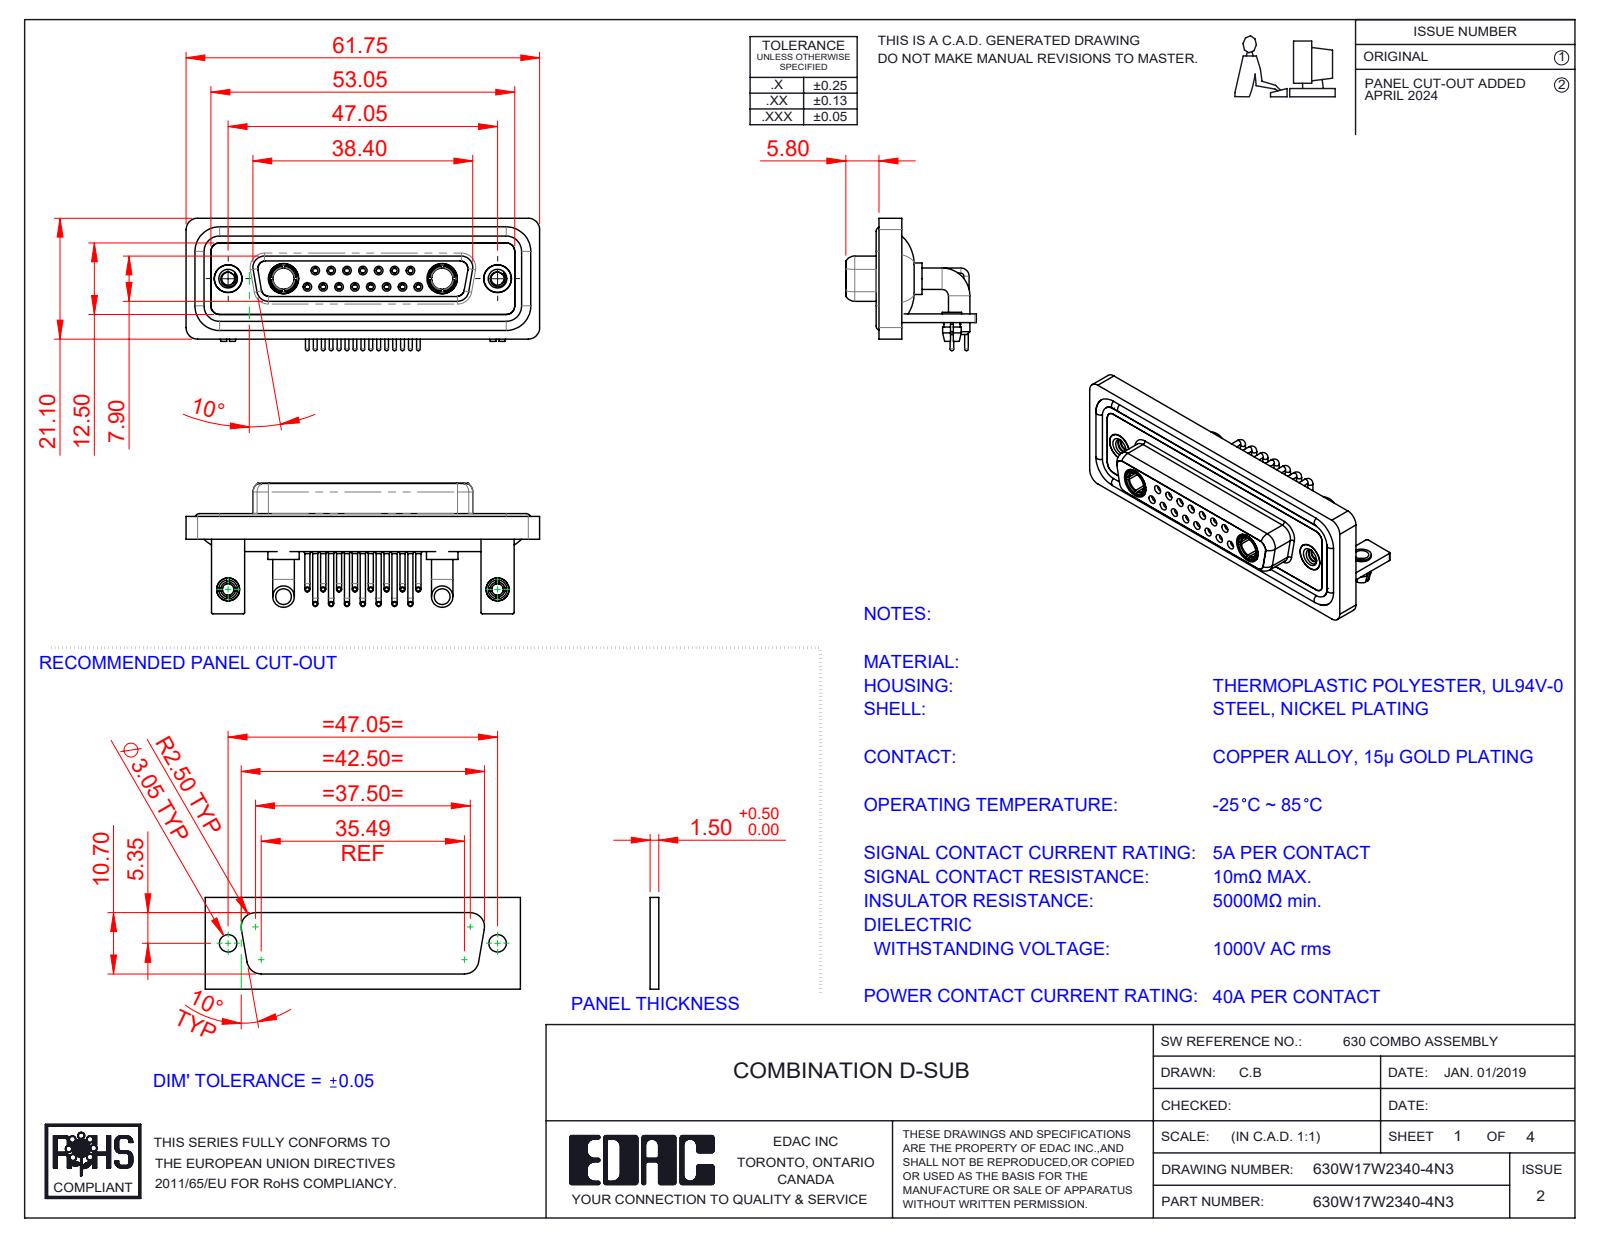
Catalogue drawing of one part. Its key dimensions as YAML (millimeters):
part_name: "Power Socket_40A RA; 630Combo Waterproof Housing_25 Contacts; 630Combo Stabilizer Bracket_50 Contacts; 630Combo Housing_17W2 (+7 more)"
step_written_by: "SolidWorks 2023 (CONFIG_CONTROL_DESIGN)"
units: millimeters
bodies: {solids: 30, faces: 1477, planar: 456, cylindrical: 639, other: 382}
overall_size: [61.75, 23.12, 22.8]
volume: 9035
surface_area: 15564
round_holes:
  - {diameter: 2, count: 17}
  - {diameter: 0.9, count: 15}
  - {diameter: 1.1, count: 15}
  - {diameter: 1.5, count: 15}
  - {diameter: 1.6, count: 8}
  - {diameter: 1.7, count: 7}
  - {diameter: 4.85, count: 4}
  - {diameter: 2.26, count: 2}
  - {diameter: 2.5, count: 2}
  - {diameter: 3.2, count: 2}
  - {diameter: 3.7, count: 2}
  - {diameter: 4, count: 2}
round_bosses_or_shafts:
  - {diameter: 0.9, count: 15}
  - {diameter: 0.65, count: 15}
  - {diameter: 1.6, count: 11}
  - {diameter: 3.75, count: 4}
  - {diameter: 5.5, count: 2}
  - {diameter: 5.2, count: 2}
  - {diameter: 4.96, count: 2}
  - {diameter: 4.95, count: 2}
partial_cylinders:
  - {radius: 2, count: 19}
  - {radius: 1.5, count: 18}
  - {radius: 0.25, count: 16}
  - {radius: 1.35, count: 8}
  - {radius: 1.6, count: 8}
  - {radius: 0.5, count: 5}
  - {radius: 0.6, count: 4}
  - {radius: 0.65, count: 4}
face_to_face_distances: [0.4, 1.8, 2.9, 3.7, 1.5, 4.1, 1.1, 1.4, 1.6, 3.1]
hole_center_spacings: [3.16, 2.77, 5.54, 8.31, 5.04, 7.49, 11.08, 5.03]
